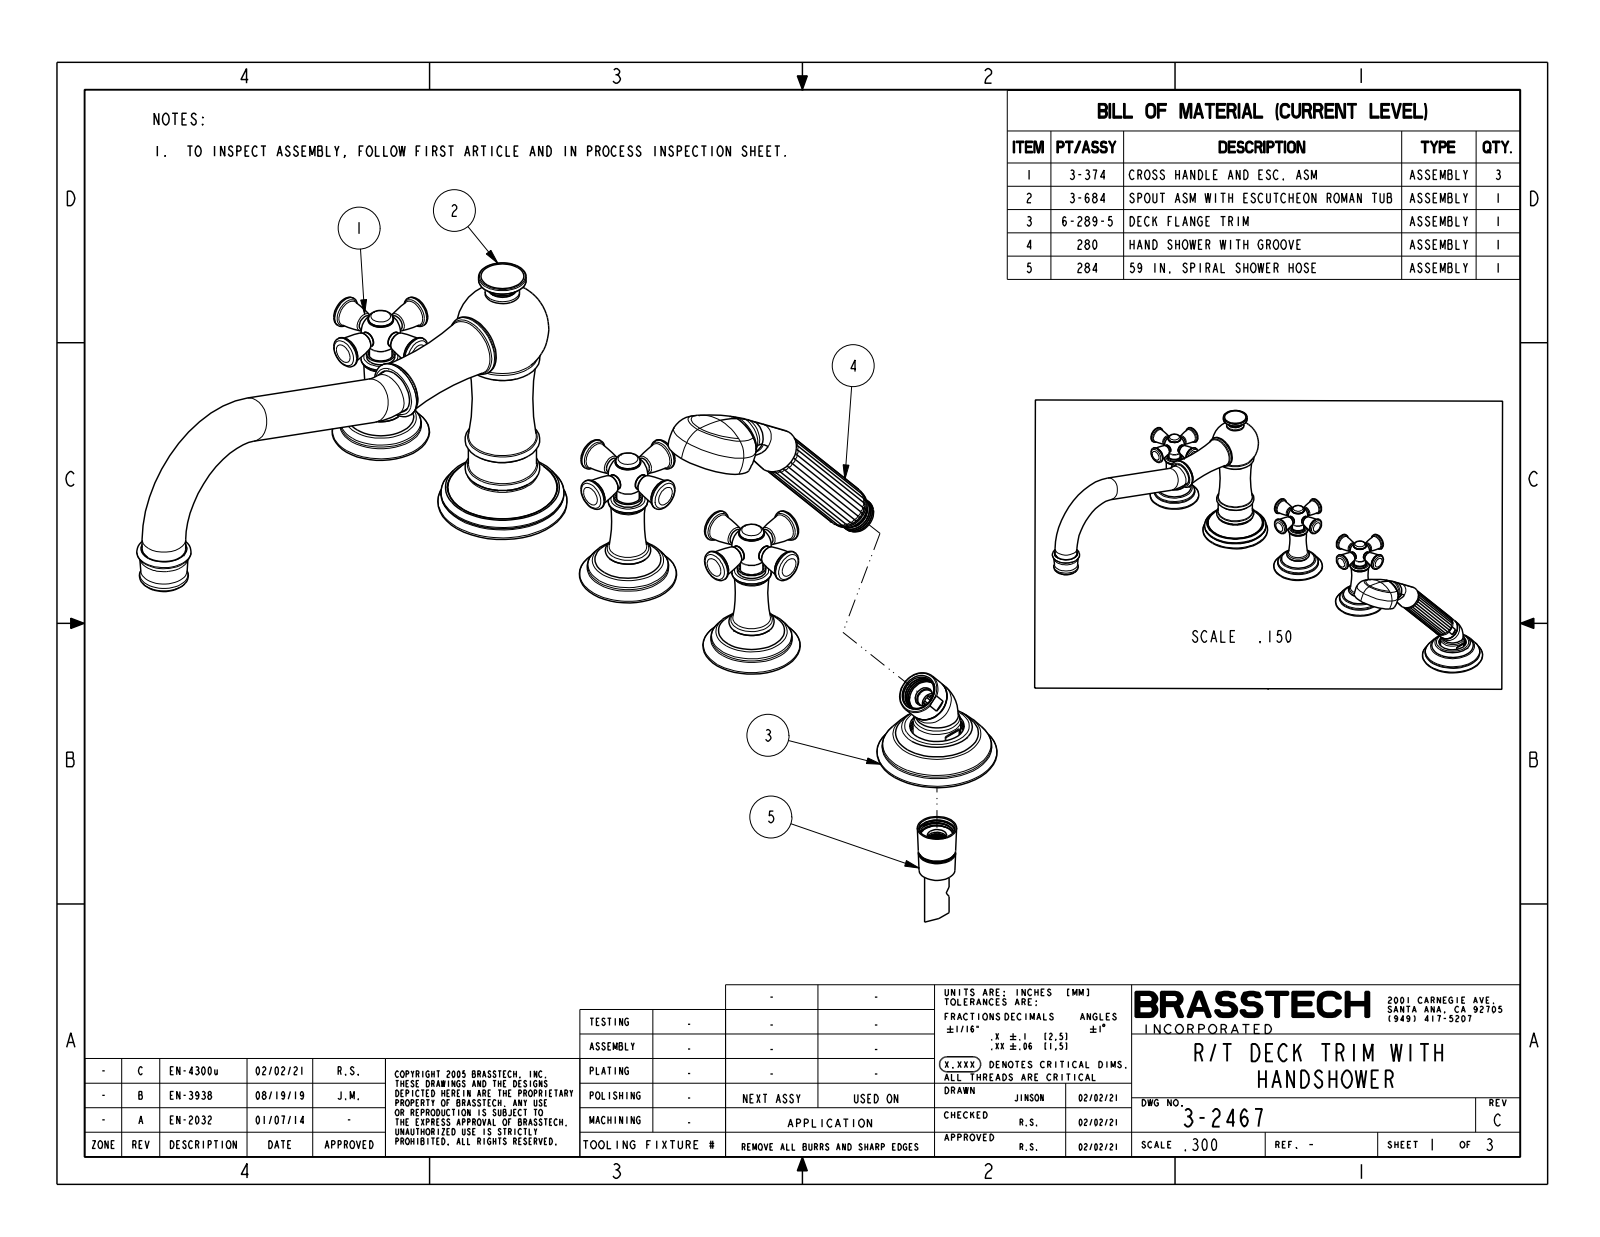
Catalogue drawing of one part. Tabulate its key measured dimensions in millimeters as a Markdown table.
| quantity | value |
| --- | --- |
| part name | 3-2467 |
| STEP written by | CREO PARAMETRIC BY PTC INC, 2018400 (CONFIG_CONTROL_DESIGN) |
| units | millimeters |
| bodies | 5 solids, 919 faces (88 planar, 212 cylindrical, 619 other) |
| overall size | 524.3 × 331.6 × 178.8 |
| volume | 768 200 mm³ |
| surface area | 129 900 mm² |
| round holes (diameter × count) | 1.2 × 52 |
| round bosses / shafts (diameter × count) | 18.3 × 4, 9.1 × 4, 25.4 × 3, 22.9 × 3, 16.5 × 3, 14.2 × 3, 13.1 × 3, 46.3 × 1 |
| partial cylindrical surfaces (radius × count) | 1.3 × 6 |
| main face-to-face distances | 19.7, 85, 65.3, 54.4, 34.7, 30.6, 56.4, 36.7, 2, 28.6 |
| hole center spacings | 9.3, 12.6, 4.7, 4.7, 4.7, 9, 4.7, 16.7 |
